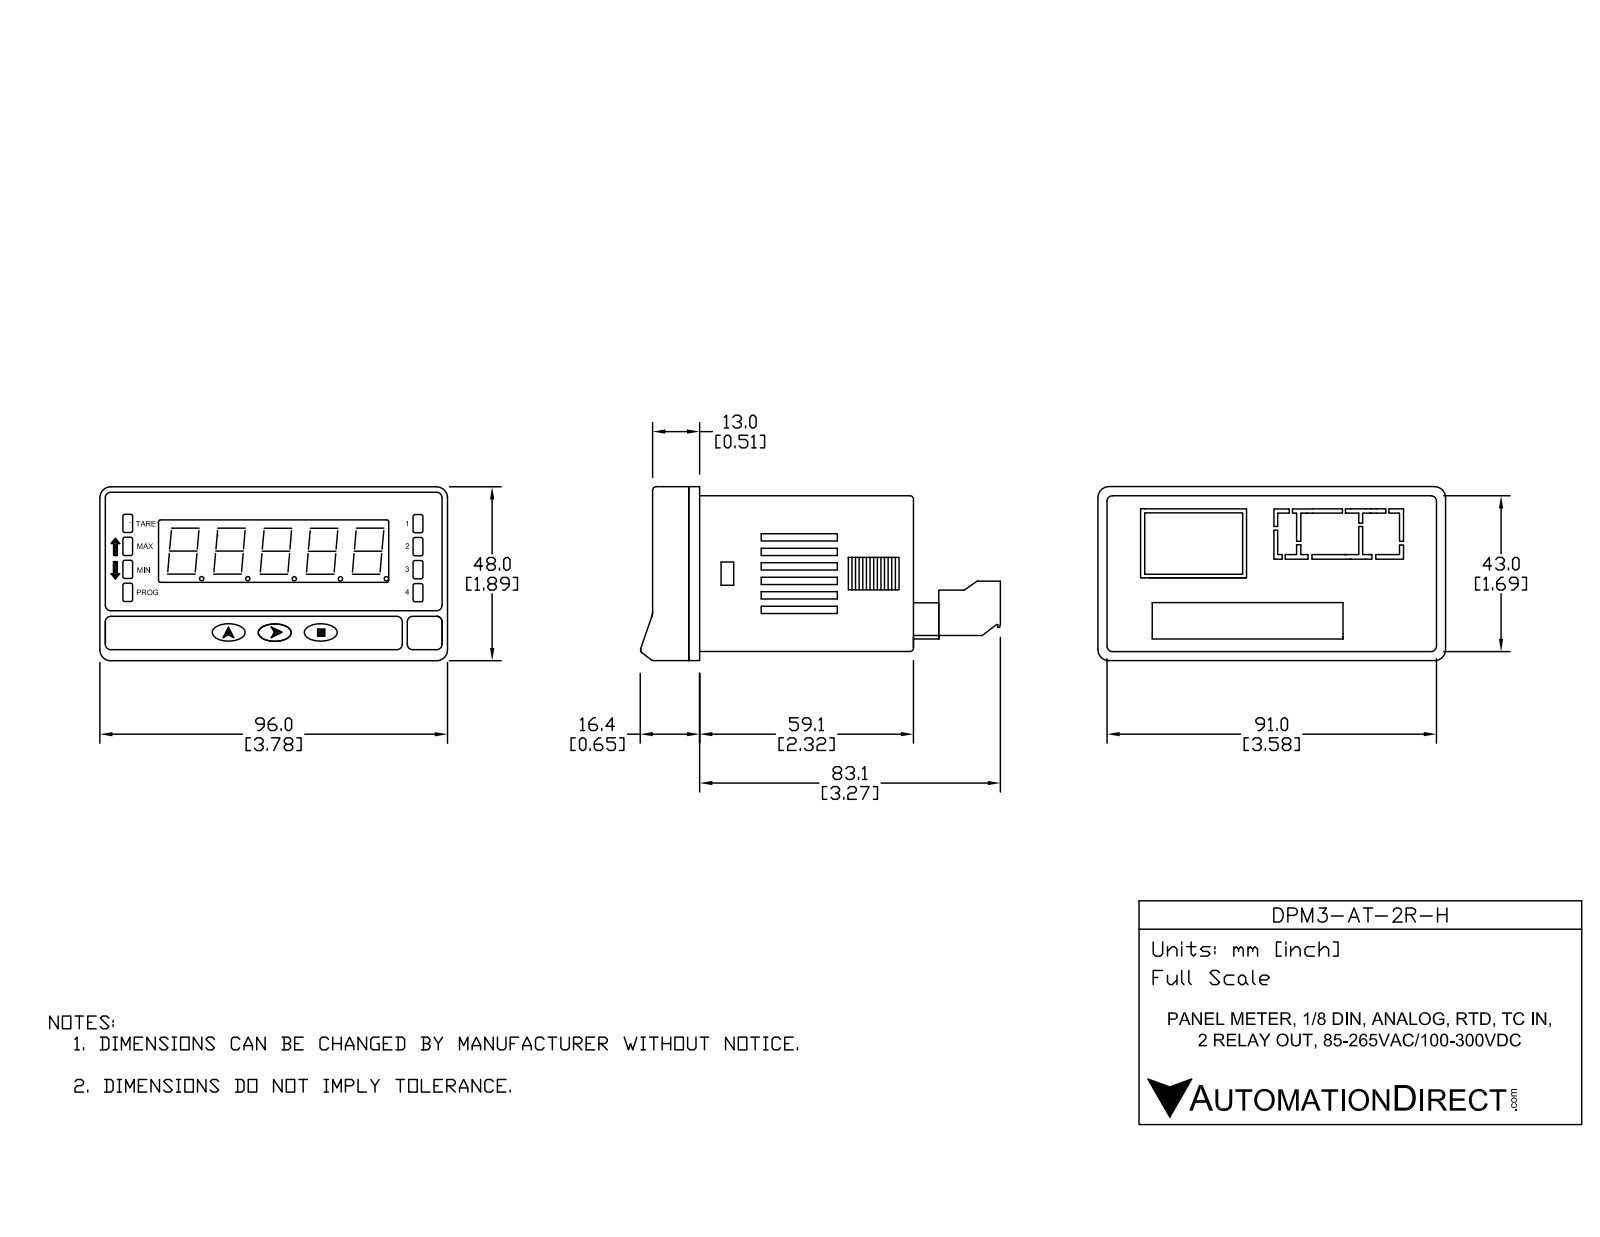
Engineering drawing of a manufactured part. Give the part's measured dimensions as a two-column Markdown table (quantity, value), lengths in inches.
| quantity | value |
| --- | --- |
| part name | DPM3-AT-2R-H |
| STEP written by | SolidWorks 2017 (AUTOMOTIVE_DESIGN) |
| units | inches |
| bodies | 10 solids, 2622 faces (2041 planar, 368 cylindrical, 213 other) |
| overall size | 3.916 × 3.78 × 1.89 |
| volume | 5.643 in³ |
| surface area | 104.7 in² |
| round holes (diameter × count) | 0.039 × 12, 0.079 × 12, 0.078 × 10, 0.118 × 10, 0.152 × 10 |
| round bosses / shafts (diameter × count) | 0.047 × 5 |
| partial cylindrical surfaces (radius × count) | 0.004 × 53, 0.02 × 42, 0.012 × 24, 0.014 × 24, 0.07 × 12, 0.072 × 12, 0.118 × 10, 0.121 × 10 |
| main face-to-face distances | 0.059, 1.634, 0.098, 1.693, 1.575, 1.732, 3.524, 0.433, 0.157, 2.78 |
| hole center spacings | 0.138, 0.276, 0.201, 0.413, 0.748, 0.197, 0.197, 0.201 |
